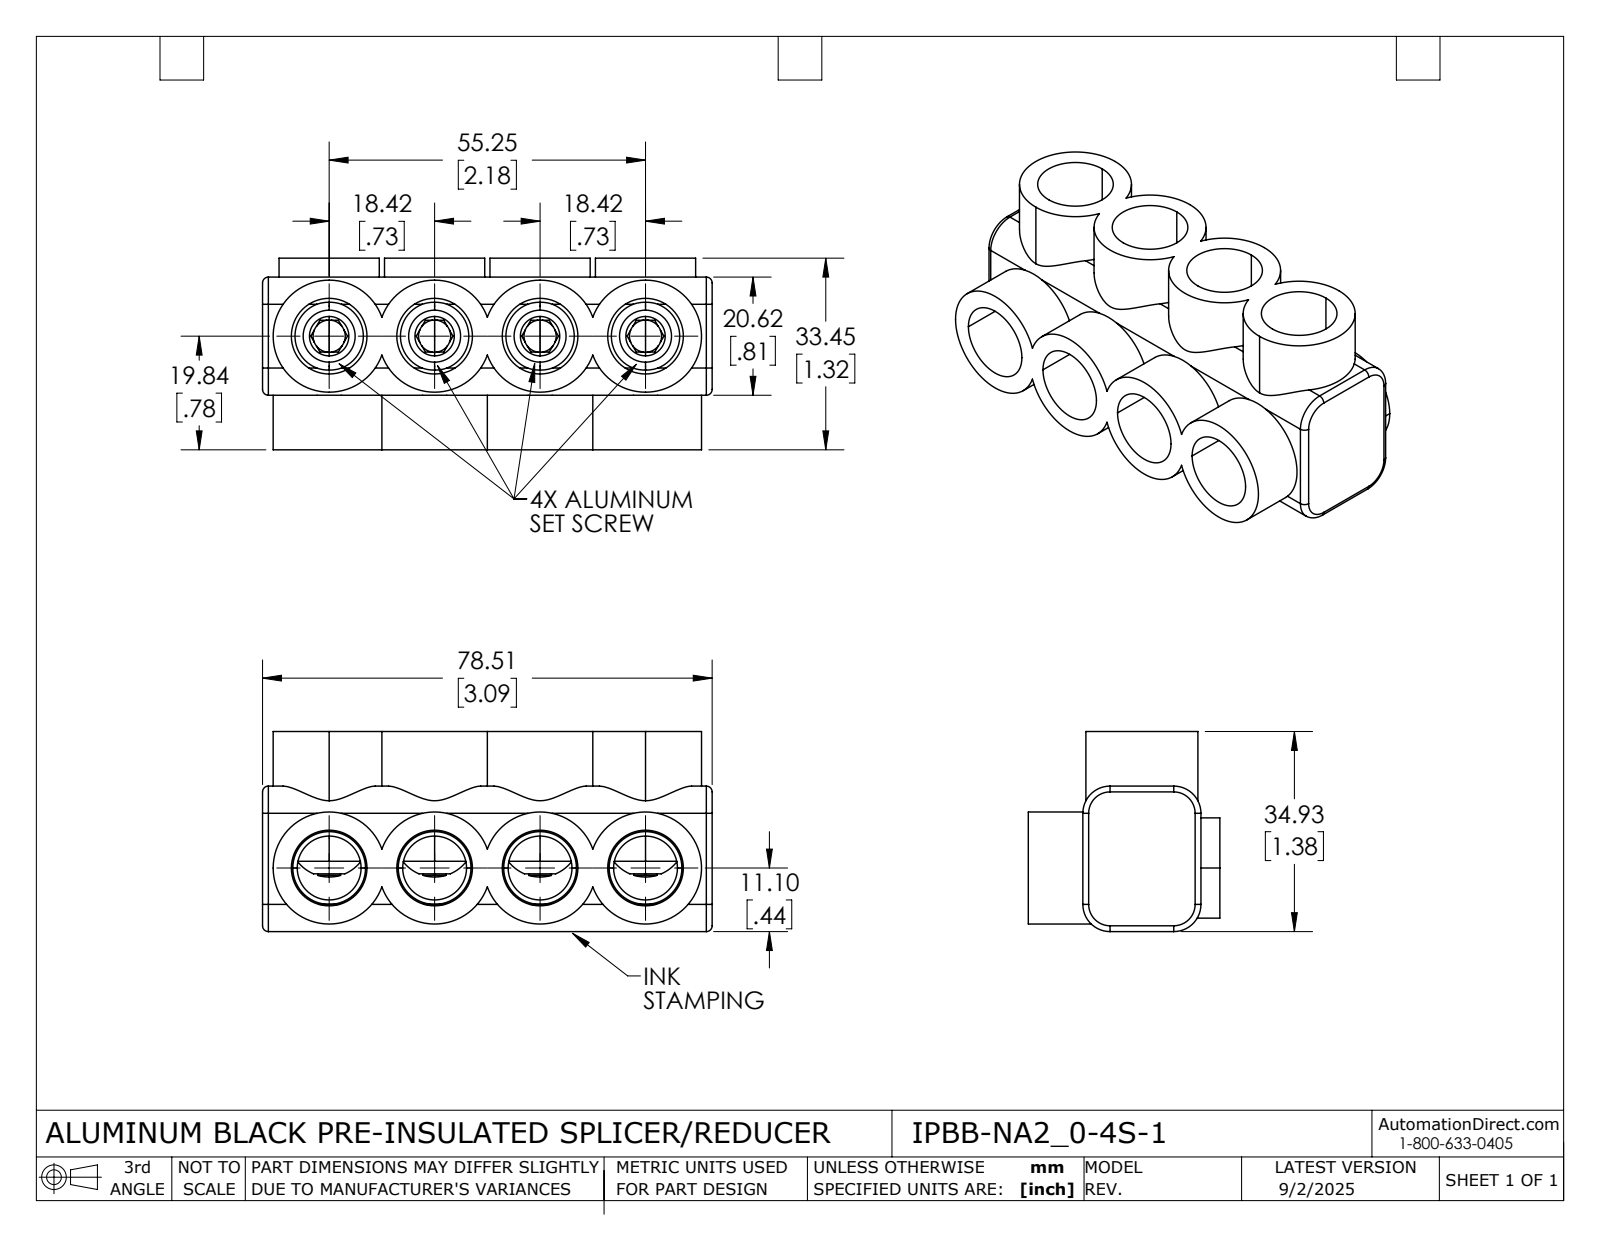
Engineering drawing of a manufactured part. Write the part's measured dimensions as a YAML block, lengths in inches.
part_name: "IPBB-NA2_0-4S-1"
step_written_by: "SolidWorks 2024 (AUTOMOTIVE_DESIGN)"
units: inches
bodies: {solids: 6, faces: 329, planar: 138, cylindrical: 119, other: 72}
overall_size: [3.091, 1.375, 1.317]
volume: 2.81
surface_area: 45.38
round_holes:
  - {diameter: 0.52, count: 8}
  - {diameter: 0.221, count: 4}
  - {diameter: 0.391, count: 4}
  - {diameter: 0.439, count: 4}
round_bosses_or_shafts:
  - {diameter: 0.77, count: 4}
  - {diameter: 0.689, count: 4}
  - {diameter: 0.437, count: 4}
  - {diameter: 0.156, count: 4}
partial_cylinders:
  - {radius: 0.04, count: 8}
  - {radius: 0.062, count: 4}
  - {radius: 0.187, count: 4}
  - {radius: 0.385, count: 4}
face_to_face_distances: [0.125, 0.5, 0.562, 0.817, 0.255, 0.125, 2.966, 0.875, 0.75, 0.13]
hole_center_spacings: [0.725, 1.45, 0.725, 2.175]
